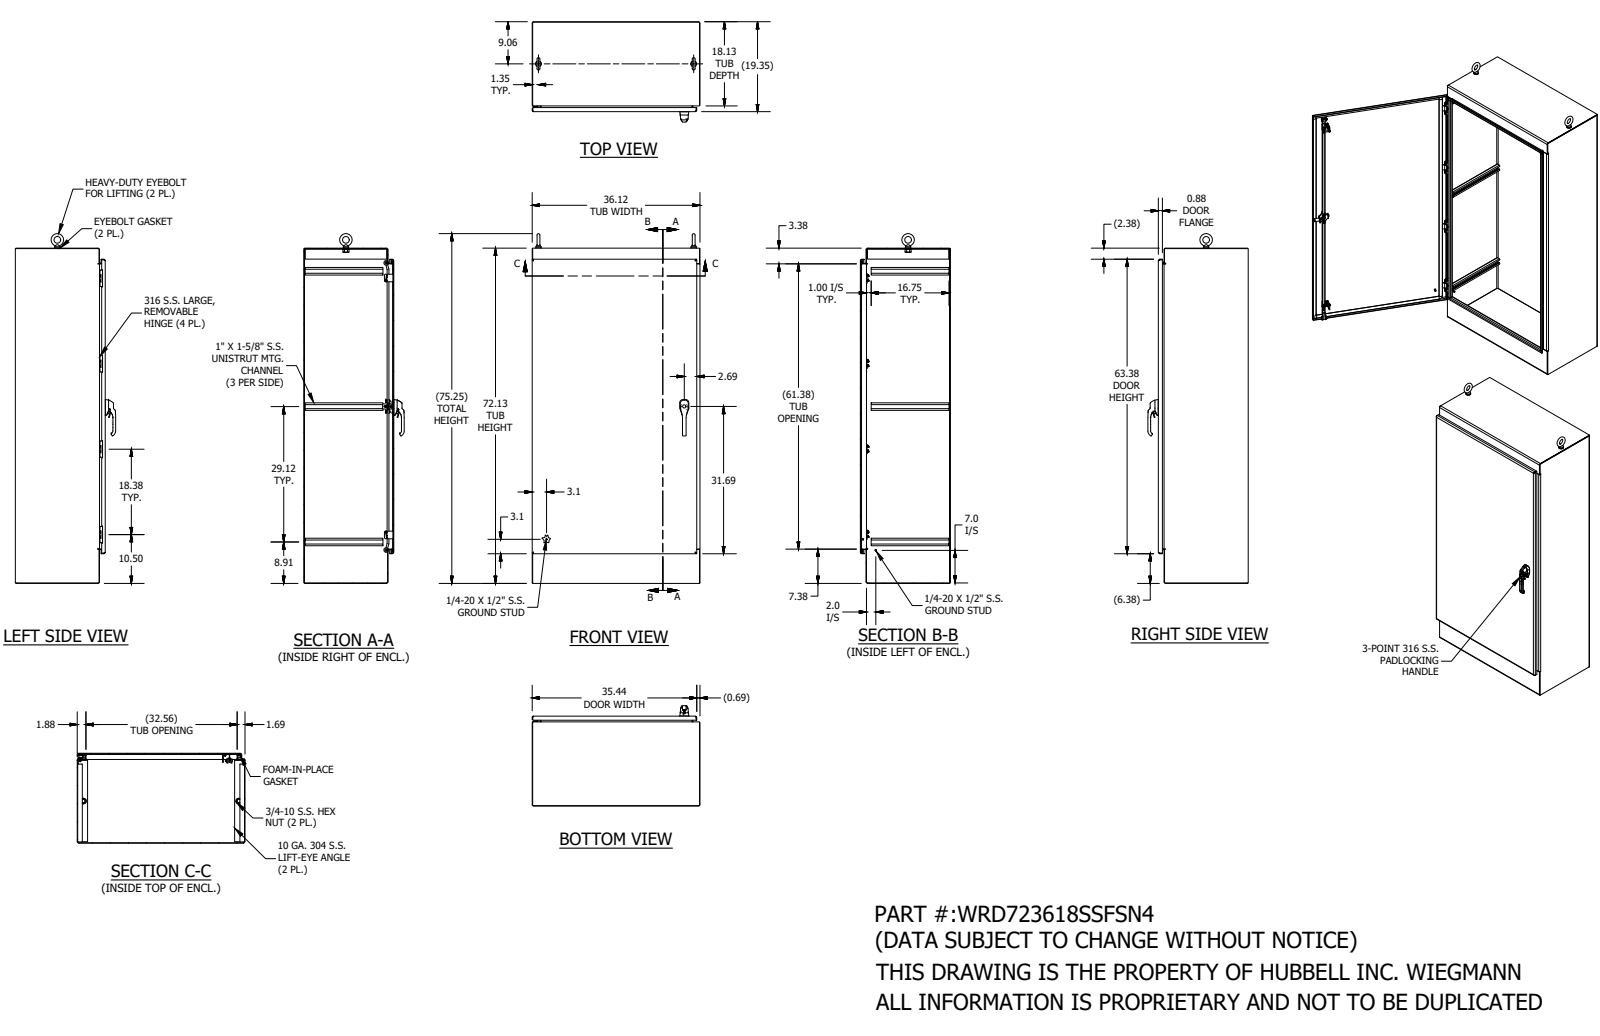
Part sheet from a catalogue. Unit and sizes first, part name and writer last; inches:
Units: inches
Overall size (bounding box): 75.248 × 36.129 × 21.598
Round holes (diameter × count): ⌀0.14 ×24, ⌀0.195 ×8, ⌀0.262 ×8, ⌀0.266 ×8, ⌀0.294 ×8, ⌀0.65 ×8, ⌀0.136 ×4, ⌀0.164 ×4, ⌀0.187 ×4, ⌀0.201 ×4, ⌀0.213 ×3, ⌀0.281 ×3
Round bosses / shafts (diameter × count): ⌀0.625 ×8, ⌀0.25 ×7, ⌀0.237 ×4, ⌀0.236 ×3, ⌀1.25 ×2, ⌀1.12 ×2, ⌀1 ×2, ⌀0.75 ×2
Partial cylindrical surfaces — rounded edges, fillets, slot ends (radius × count): R0.02 ×172, R0.012 ×114, R0.125 ×34, R0.019 ×21, R0.062 ×18, R0.05 ×14, R0.063 ×14, R0.079 ×14
Main face-to-face distances: 0.104, 36.021, 19.245, 19.141, 19.349, 19.245, 0.104, 35.917, 72.021, 36.125
Hole centre spacings: 0.018, 0.023, 0.029, 0.38, 0.76, 1, 18.375, 36.75
Volume: 1 153 in³ · Surface area: 21 493 in²
Bodies: 103 solids, 3881 faces (1580 planar, 1362 cylindrical, 939 other)
Part name (STEP PRODUCT): WRD723618SSFSN4
STEP written by: SolidWorks 2019 (AUTOMOTIVE_DESIGN)
